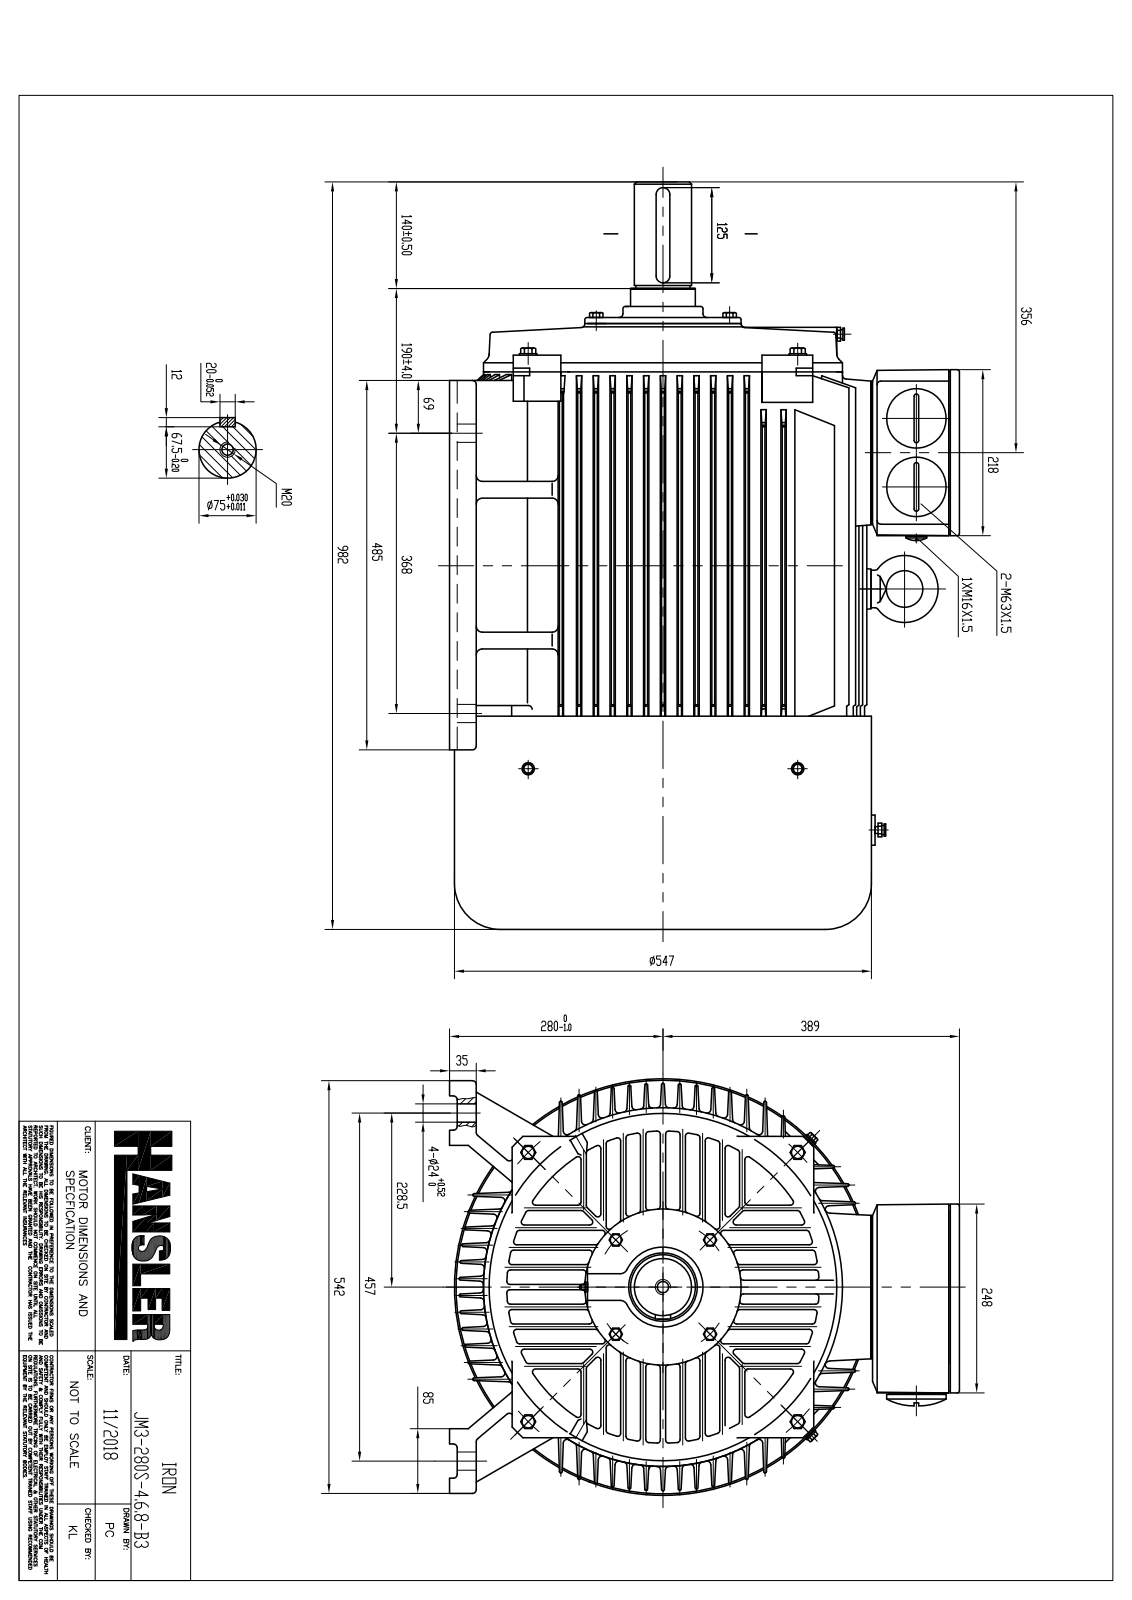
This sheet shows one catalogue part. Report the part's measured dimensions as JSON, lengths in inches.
{"part_name": "pc0534AA92lz0z", "step_written_by": "SIEMENS PLM Software NX 8.5 (AUTOMOTIVE_DESIGN)", "units": "inches", "bodies": {"solids": 59, "faces": 6586, "planar": 4651, "cylindrical": 950, "other": 985}, "overall_size": [37.815, 26.291, 21.535], "volume_in3": 2406, "surface_area_in2": 11990, "round_holes": [[0.394, 10], [0.472, 9], [0.945, 5], [0.315, 4], [0.33, 4], [0.331, 4], [0.441, 4], [0.494, 4], [0.496, 4], [0.551, 4], [0.571, 4], [1.705, 2]], "round_bosses_or_shafts": [[0.738, 4], [0.63, 4], [0.496, 4], [0.472, 4], [0.428, 4], [0.394, 4], [0.356, 4], [0.315, 4]], "partial_cylinders_radius": [[0.197, 98], [0.157, 82], [0.079, 68], [0.394, 16], [1.575, 9], [0.315, 8], [16.437, 5], [0.039, 4]], "face_to_face_distances": [25.709, 2.475, 22.514, 3.346, 0.534, 24.455, 1.941, 21.98, 0.36, 0.894], "hole_center_spacings": [8.071, 4.035, 5.807, 5.707, 13.878, 10.637, 5.707, 5.709]}
